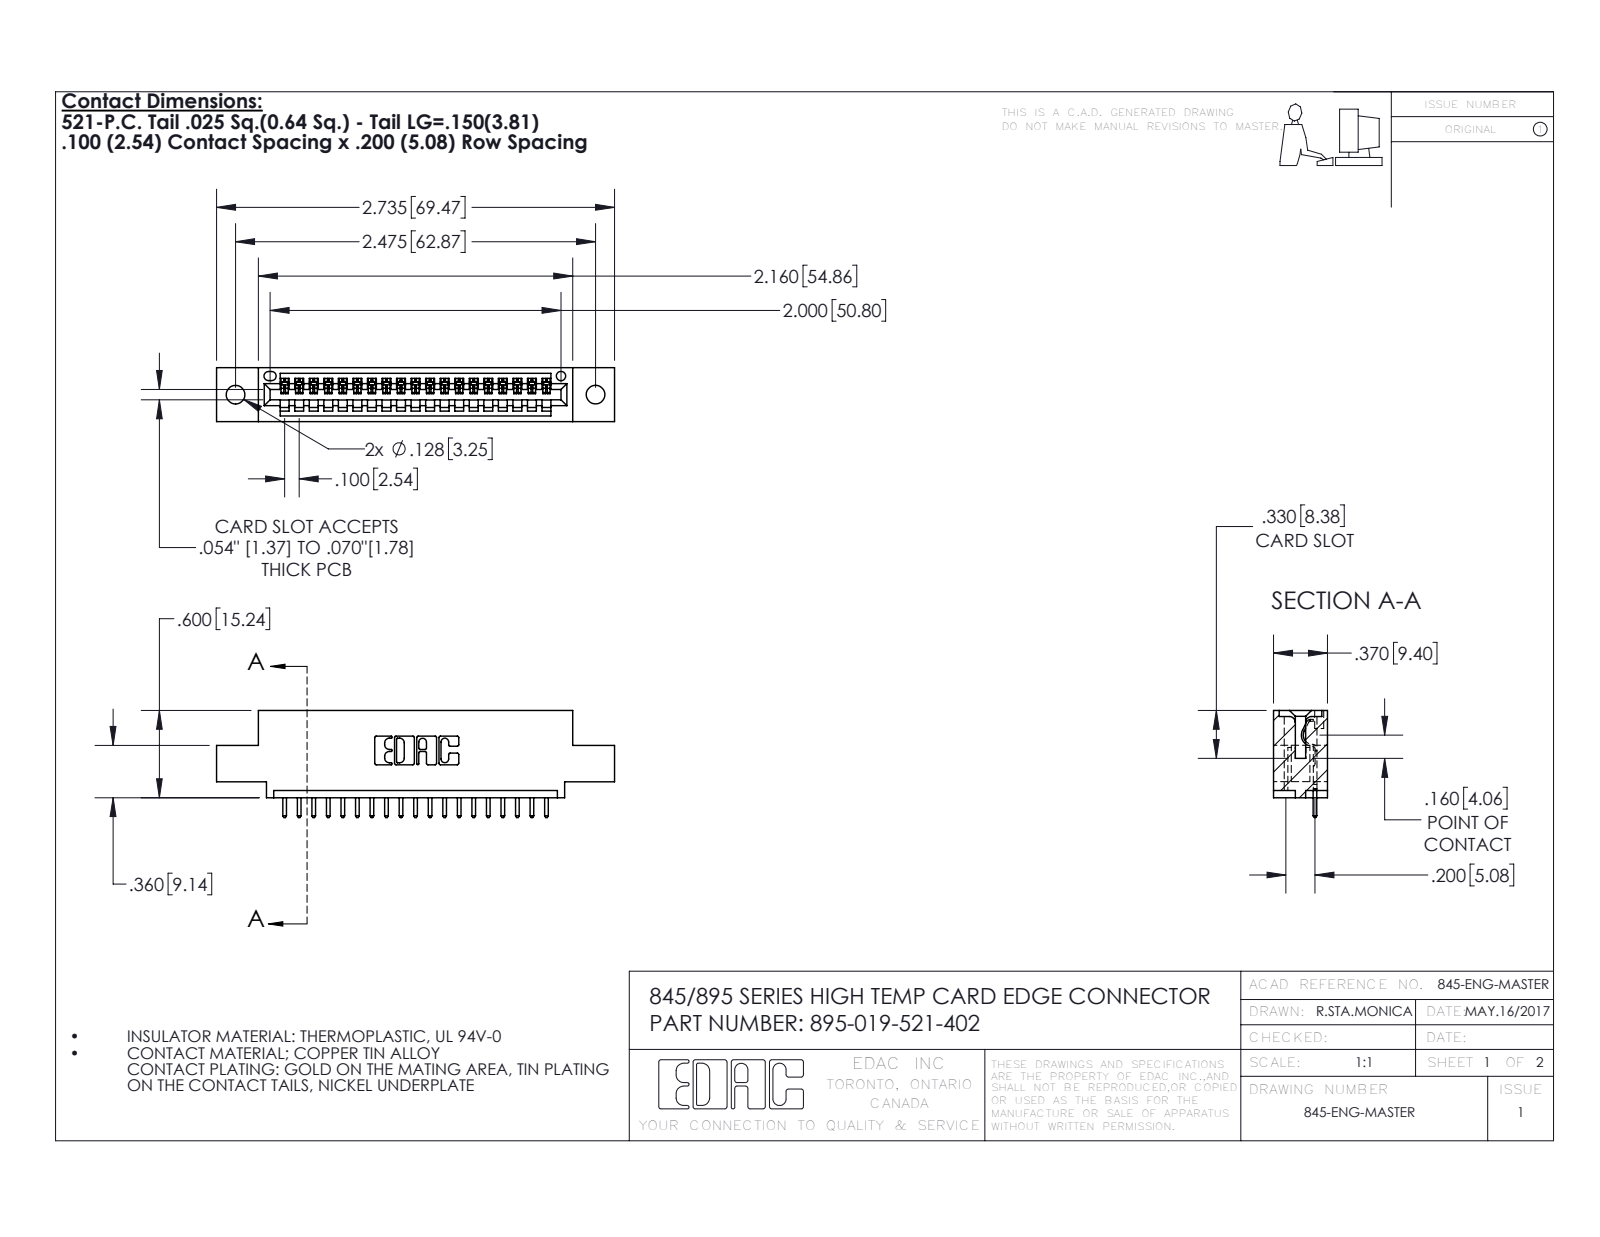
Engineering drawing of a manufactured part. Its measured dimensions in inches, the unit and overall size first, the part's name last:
Units: inches
Overall size (bounding box): 2.735 × 0.737 × 0.37
Round holes (diameter × count): ⌀0.128 ×2, ⌀0.064 ×1
Partial cylindrical surfaces — rounded edges, fillets, slot ends (radius × count): R0.006 ×38, R0.01 ×38, R0.01 ×22, R0.007 ×6, R0.031 ×6, R0.026 ×3, R0.031 ×2, R0.04 ×2
Main face-to-face distances: 0.072, 0.298, 0.37, 0.2, 0.098, 0.272, 0.025, 0.225, 0.149, 0.6
Hole centre spacings: 0.27, 2.241, 2.475
Volume: 0.381 in³ · Surface area: 11.76 in²
Bodies: 20 solids, 1232 faces (844 planar, 388 cylindrical, 0 other)
Part name (STEP PRODUCT): 345-292-001_345-293-121; 395-019-521-402; 345 Part_0.110 Offset - 0.128 Dia
STEP written by: SolidWorks 2016 (CONFIG_CONTROL_DESIGN)
